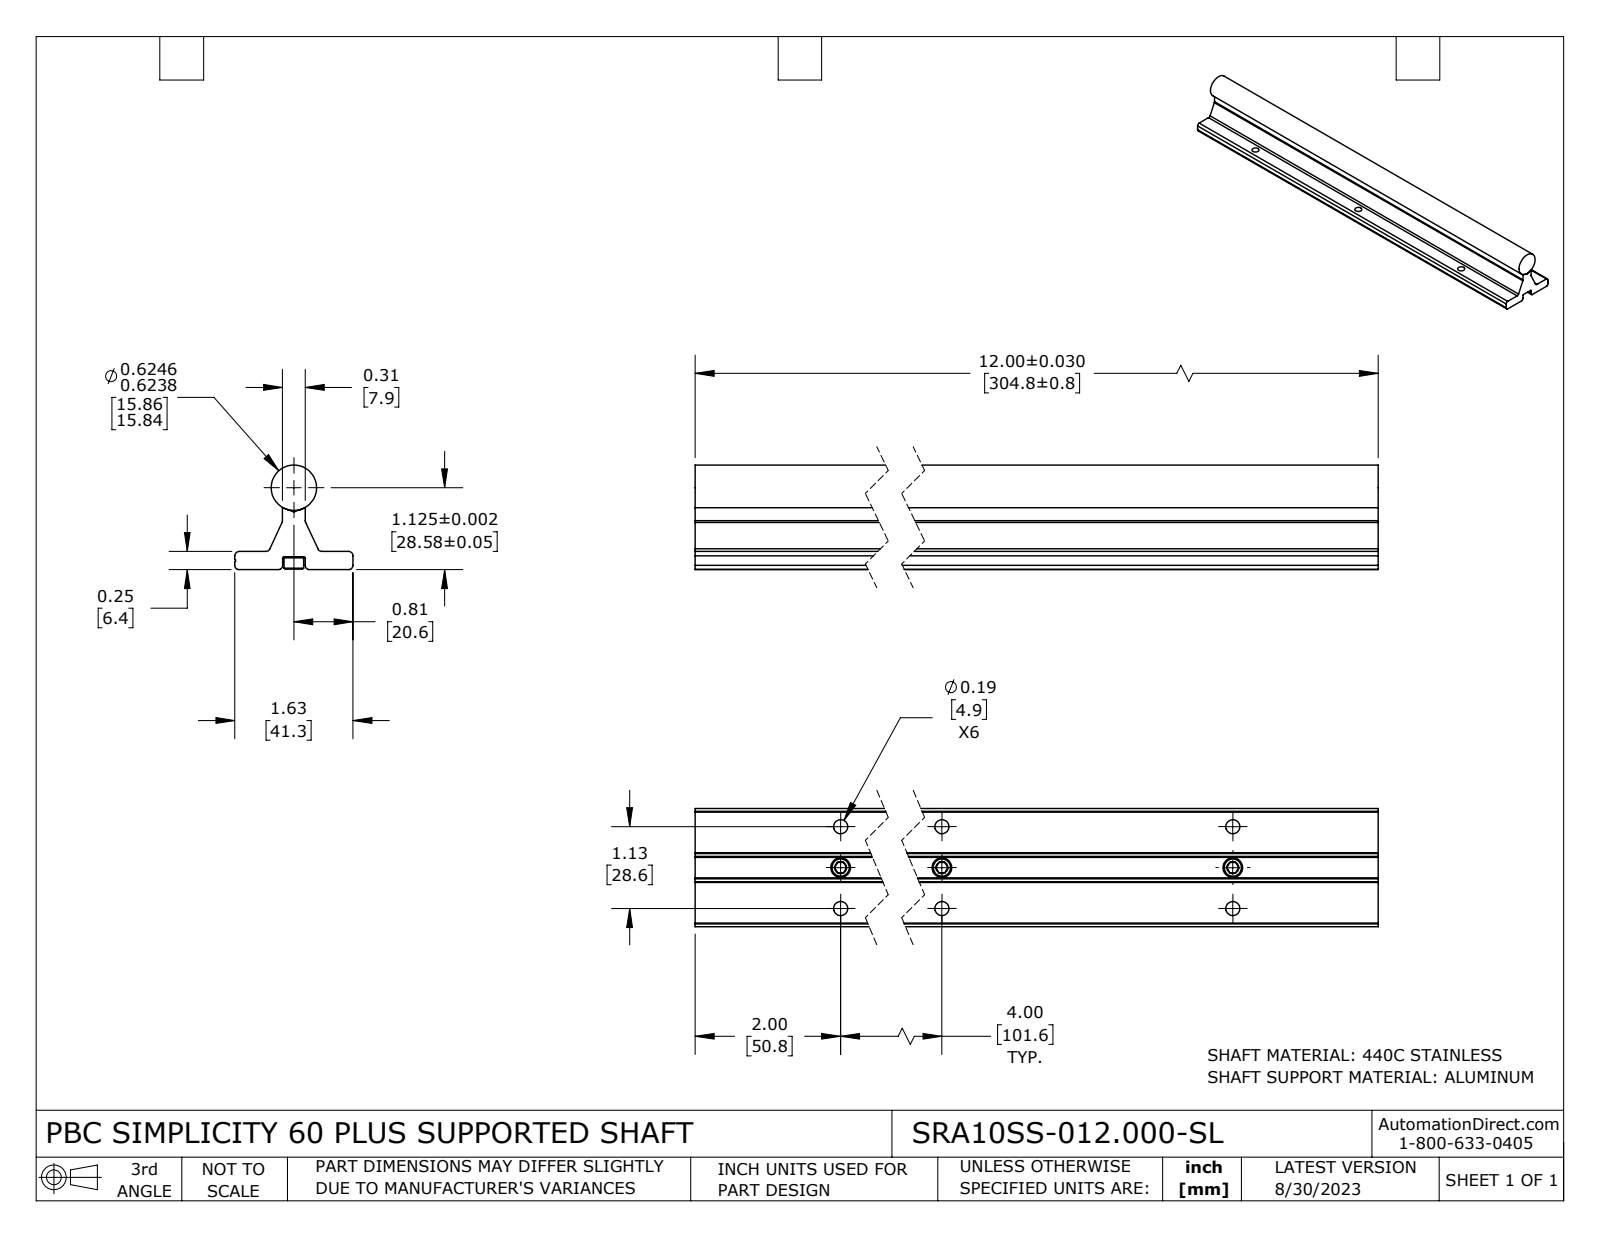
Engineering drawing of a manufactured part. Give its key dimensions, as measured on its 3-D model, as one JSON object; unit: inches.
{"part_name": "SRA10SS-012.000-SL", "step_written_by": "SolidWorks 2021 (CONFIG_CONTROL_DESIGN)", "units": "inches", "bodies": {"solids": 5, "faces": 161, "planar": 60, "cylindrical": 56, "other": 45}, "overall_size": [12, 1.625, 1.438], "volume_in3": 10.89, "surface_area_in2": 87.98, "round_holes": [[0.194, 9], [0.141, 3], [0.188, 3]], "round_bosses_or_shafts": [[0.27, 3], [0.165, 3], [0.625, 1]], "partial_cylinders_radius": [[0.06, 6], [0.015, 2], [0.062, 2], [0.063, 2]], "face_to_face_distances": [0.25, 0.174, 0.076, 0.656, 0.969, 0.657, 0.968, 0.311, 0.313, 1.625], "hole_center_spacings": [4.039, 0.563, 4, 4.155, 8.02, 1.125, 8, 8.079]}
